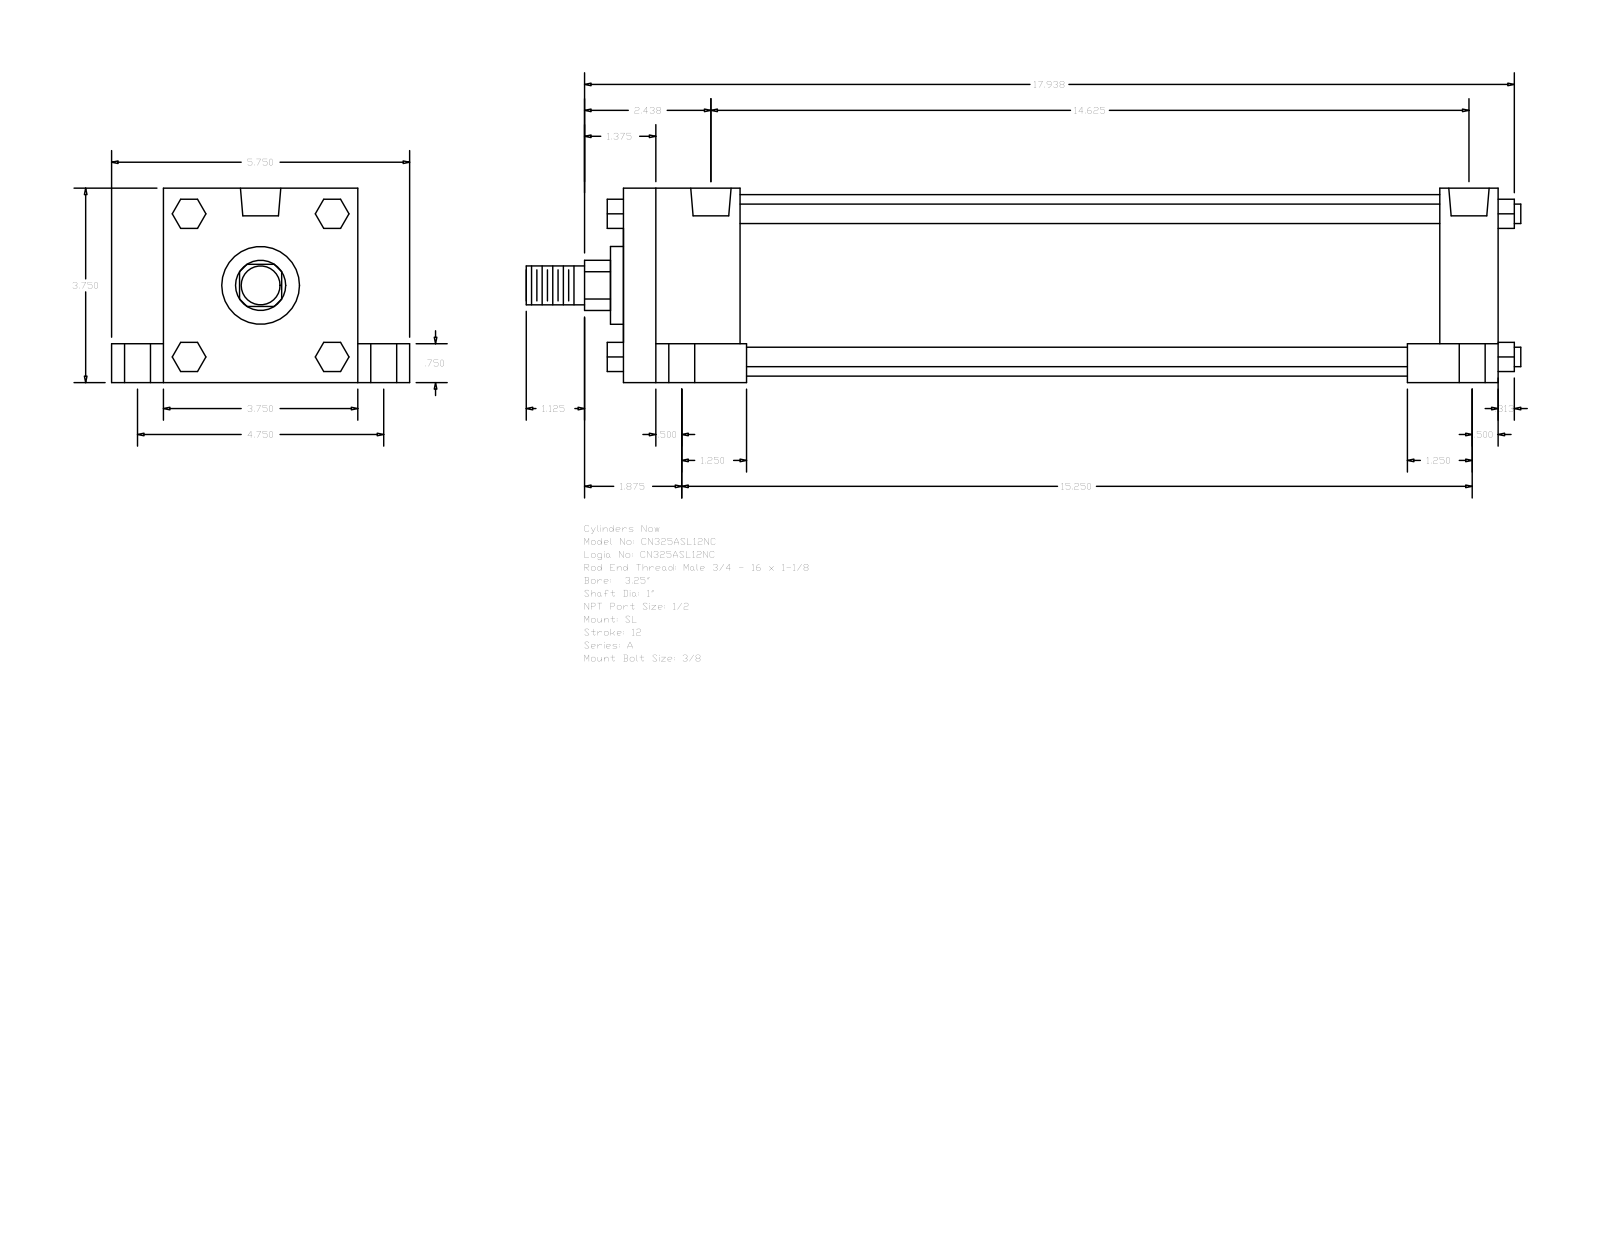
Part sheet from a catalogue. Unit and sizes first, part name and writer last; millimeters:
Units: millimetres
Overall size (bounding box): 487.36 × 146.05 × 95.25
Round holes (diameter × count): ⌀8.73 ×4, ⌀12.7 ×4, ⌀19.05 ×4, ⌀19.77 ×2
Round bosses / shafts (diameter × count): ⌀9.53 ×4, ⌀88.9 ×1, ⌀38.1 ×1, ⌀25.4 ×1, ⌀19.05 ×1
Partial cylindrical surfaces — rounded edges, fillets, slot ends (radius × count): R12.29 ×1
Main face-to-face distances: 95.24, 428.63, 19.05, 25.41, 120.65, 76.19, 57.15, 400.05, 342.9, 371.48
Hole centre spacings: 3.18, 60.35, 60.52, 62, 62.81, 120.66, 365.12, 368.3
Bodies: 0 solids, 150 faces (114 planar, 36 cylindrical, 0 other)
Part name (STEP PRODUCT): A_SL__0325_1
STEP written by: GSSL Pune (CONFIG_CONTROL_DESIGN)
